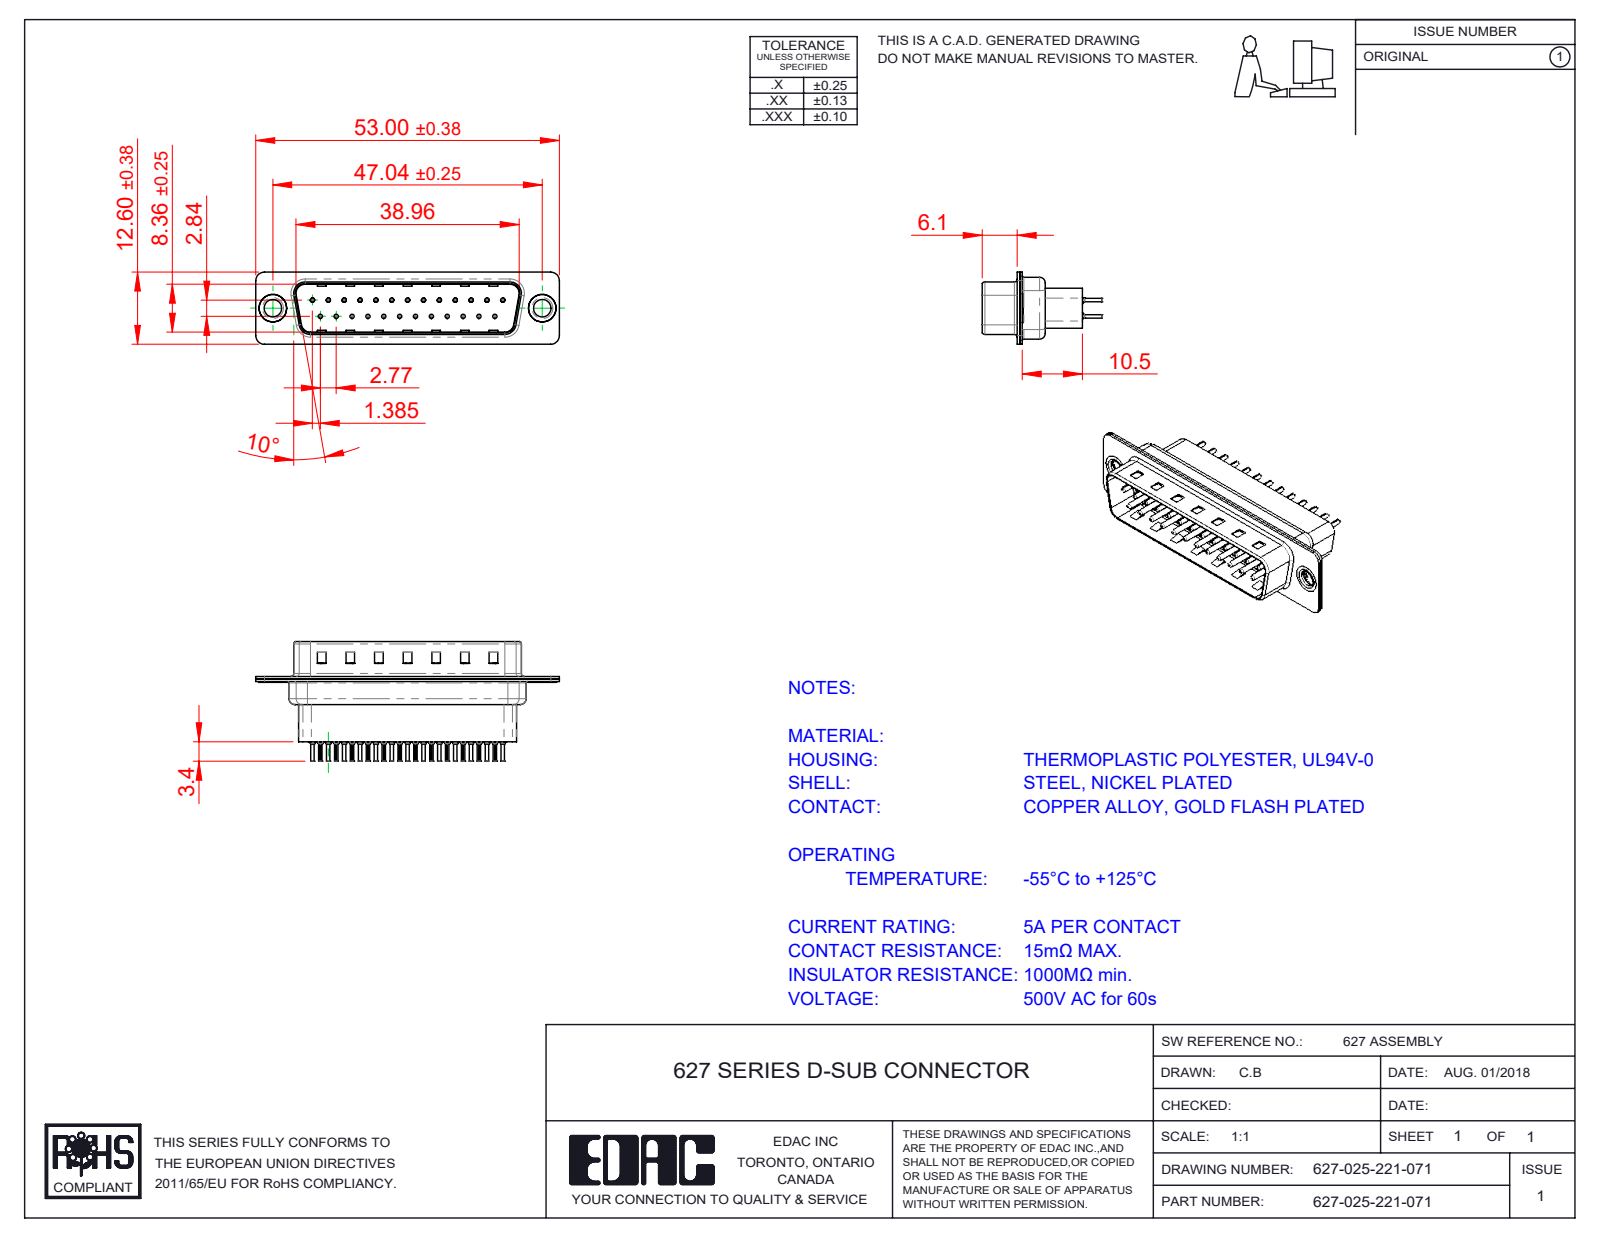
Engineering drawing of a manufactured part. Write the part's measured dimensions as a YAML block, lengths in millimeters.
part_name: "627 Housing_25 HP; 627 Contact Row 2_21H; 627 Shell Rear_25 Contacts; 627-025-221-071 (+3 more)"
step_written_by: "SolidWorks 2020 (CONFIG_CONTROL_DESIGN)"
units: millimeters
bodies: {solids: 30, faces: 2800, planar: 771, cylindrical: 1046, other: 983}
overall_size: [53, 20.8, 12.6]
volume: 3720
surface_area: 9633
round_holes:
  - {diameter: 0.2, count: 25}
  - {diameter: 0.35, count: 25}
  - {diameter: 1.1, count: 25}
  - {diameter: 1.6, count: 25}
  - {diameter: 3.05, count: 2}
  - {diameter: 4, count: 2}
  - {diameter: 4.8, count: 2}
round_bosses_or_shafts:
  - {diameter: 2, count: 25}
  - {diameter: 1.5, count: 25}
  - {diameter: 0.75, count: 25}
  - {diameter: 0.6, count: 25}
  - {diameter: 5, count: 2}
  - {diameter: 4.9, count: 2}
  - {diameter: 3.55, count: 2}
partial_cylinders:
  - {radius: 0.1, count: 50}
  - {radius: 1.5, count: 16}
  - {radius: 2, count: 12}
  - {radius: 0.5, count: 8}
  - {radius: 1.6, count: 8}
  - {radius: 0.25, count: 4}
  - {radius: 0.6, count: 4}
  - {radius: 0.65, count: 4}
face_to_face_distances: [0.4, 0.45, 0.82, 9.58, 0.68, 7.68, 0.9, 1.5, 1.08, 8.08]
hole_center_spacings: [3.16, 8.31, 2.77, 5.54, 11.08, 16.62, 5.03, 5.04]
